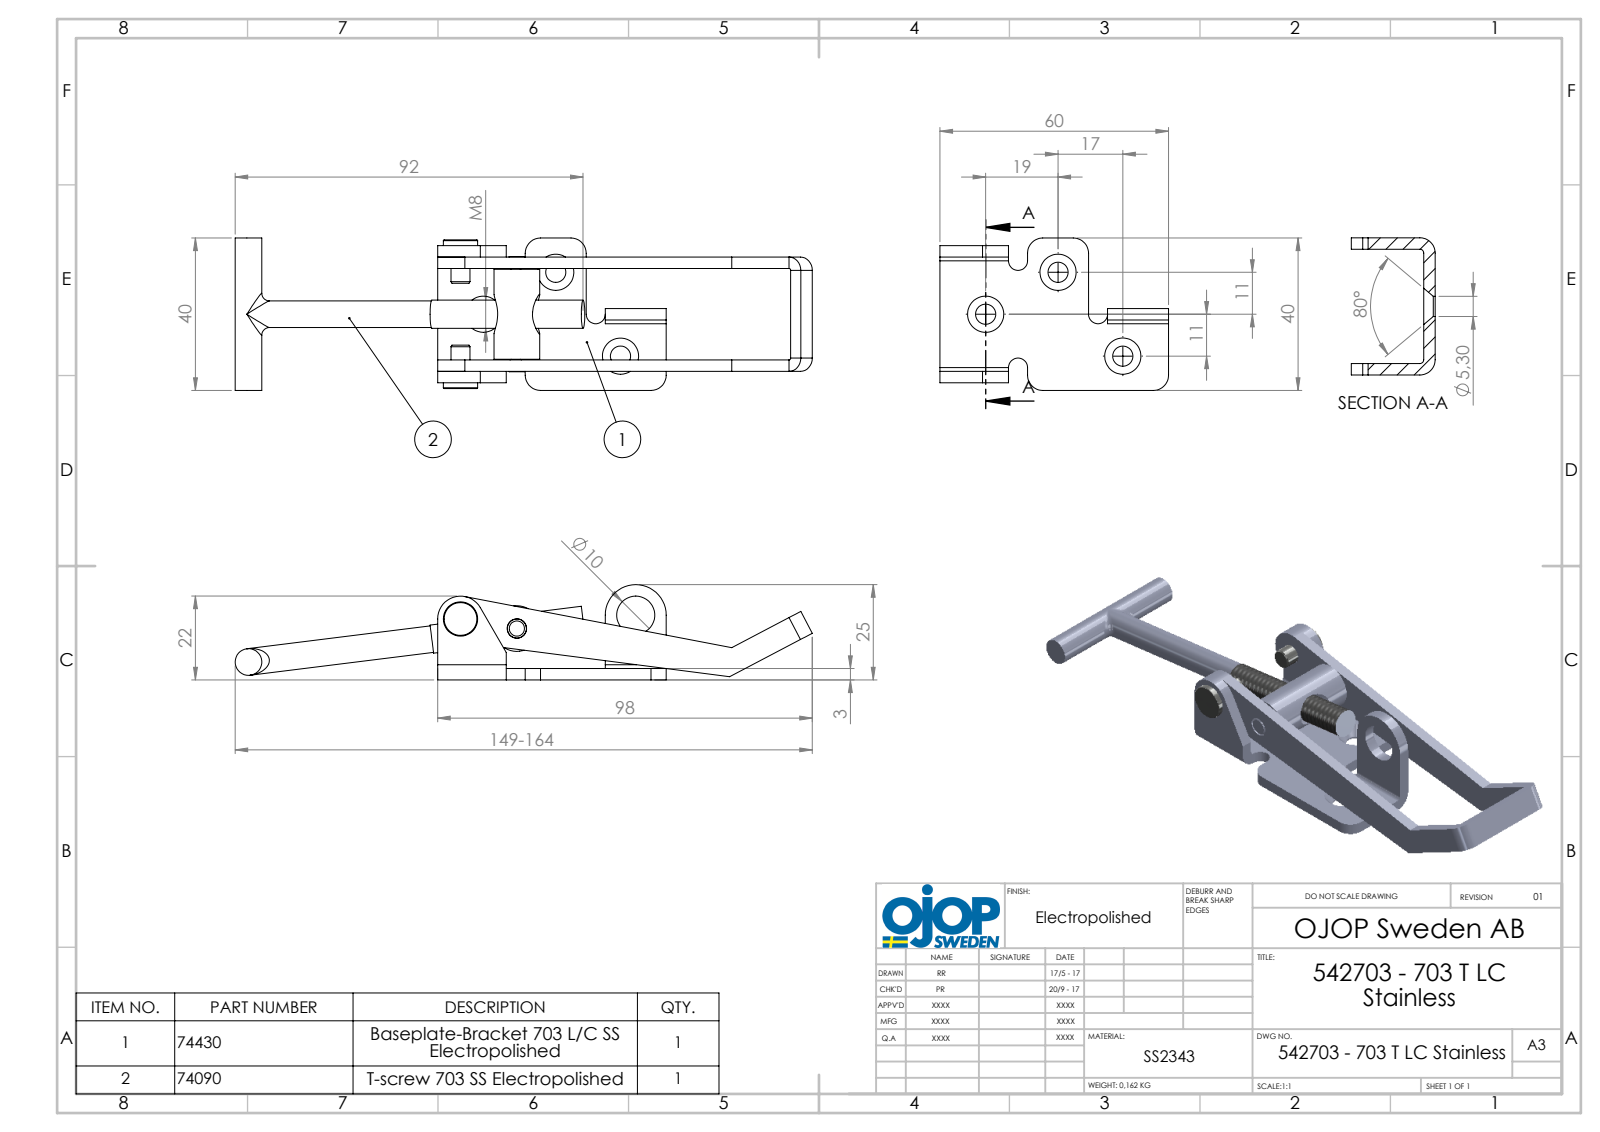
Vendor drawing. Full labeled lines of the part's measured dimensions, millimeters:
Part name (STEP PRODUCT): 542703 - 703 T LC Stainless; 703 - Rulle RF; 703 - T-skruv; 703 RF - Bygel (+2 more)
STEP written by: SolidWorks 2015 (AUTOMOTIVE_DESIGN)
Units: millimetres
Bodies: 6 solids, 158 faces (66 planar, 72 cylindrical, 20 other)
Overall size (bounding box): 150.26 × 40.05 × 25
Volume: 20 705 mm³ · Surface area: 16 329 mm²
Round holes (diameter × count): ⌀5.3 ×3, ⌀5.1 ×2, ⌀7.2 ×2, ⌀10 ×1
Round bosses / shafts (diameter × count): ⌀7 ×3, ⌀5 ×2, ⌀12 ×1, ⌀9 ×1, ⌀7.4 ×1
Partial cylindrical surfaces — rounded edges, fillets, slot ends (radius × count): R4 ×7, R1 ×3, R2.5 ×3, R0.5 ×2, R3.5 ×2, R6 ×1, R8 ×1
Main face-to-face distances: 3, 27, 30, 16.5, 13.5, 24, 6, 33, 19.5, 10.5
Hole centre spacings: 15.01, 21.95, 27.8, 31.4, 37.64, 46.01
